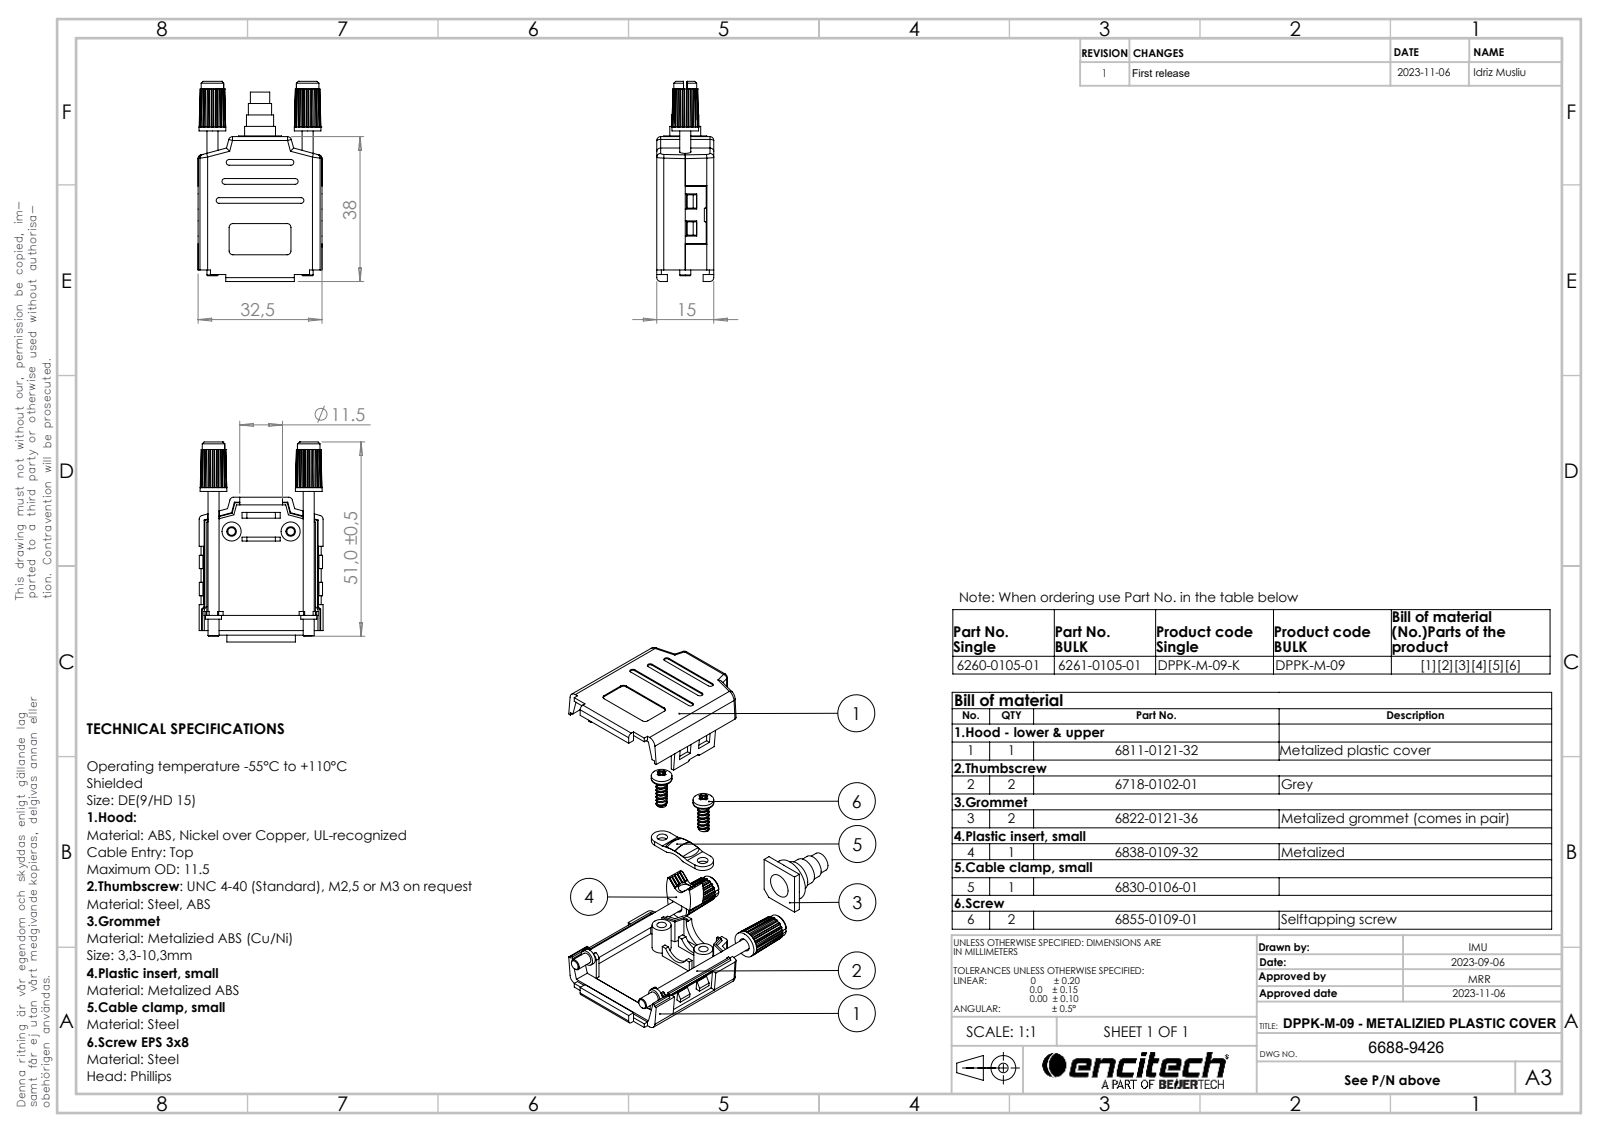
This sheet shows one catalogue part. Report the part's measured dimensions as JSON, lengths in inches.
{"part_name": "6811-0121-32 (part. 1); 6838-0109-32; 6811-0121-32 (part. 2); 6830-0106-01 (+4 more)", "step_written_by": "SolidWorks 2021 (AUTOMOTIVE_DESIGN)", "units": "inches", "bodies": {"solids": 11, "faces": 844, "planar": 586, "cylindrical": 167, "other": 91}, "overall_size": [2.067, 1.28, 0.588], "volume_in3": 0.483, "surface_area_in2": 17.95, "round_holes": [[0.079, 2], [0.098, 2], [0.11, 2], [0.138, 2], [0.177, 1], [0.217, 1], [0.256, 1]], "round_bosses_or_shafts": [[0.276, 2], [0.236, 2], [0.215, 2], [0.197, 2], [0.165, 2], [0.118, 2], [0.114, 2], [0.445, 1]], "partial_cylinders_radius": [[0.039, 22], [0.03, 7], [0.02, 6], [0.079, 5], [0.01, 4], [0.059, 4], [0.013, 2], [0.057, 2]], "face_to_face_distances": [0.067, 0.521, 0.588, 0.454, 0.055, 0.576, 0.509, 0.047, 0.227, 1.274], "hole_center_spacings": [0.298, 0.306, 0.308, 0.591, 0.599, 0.602, 0.61]}
